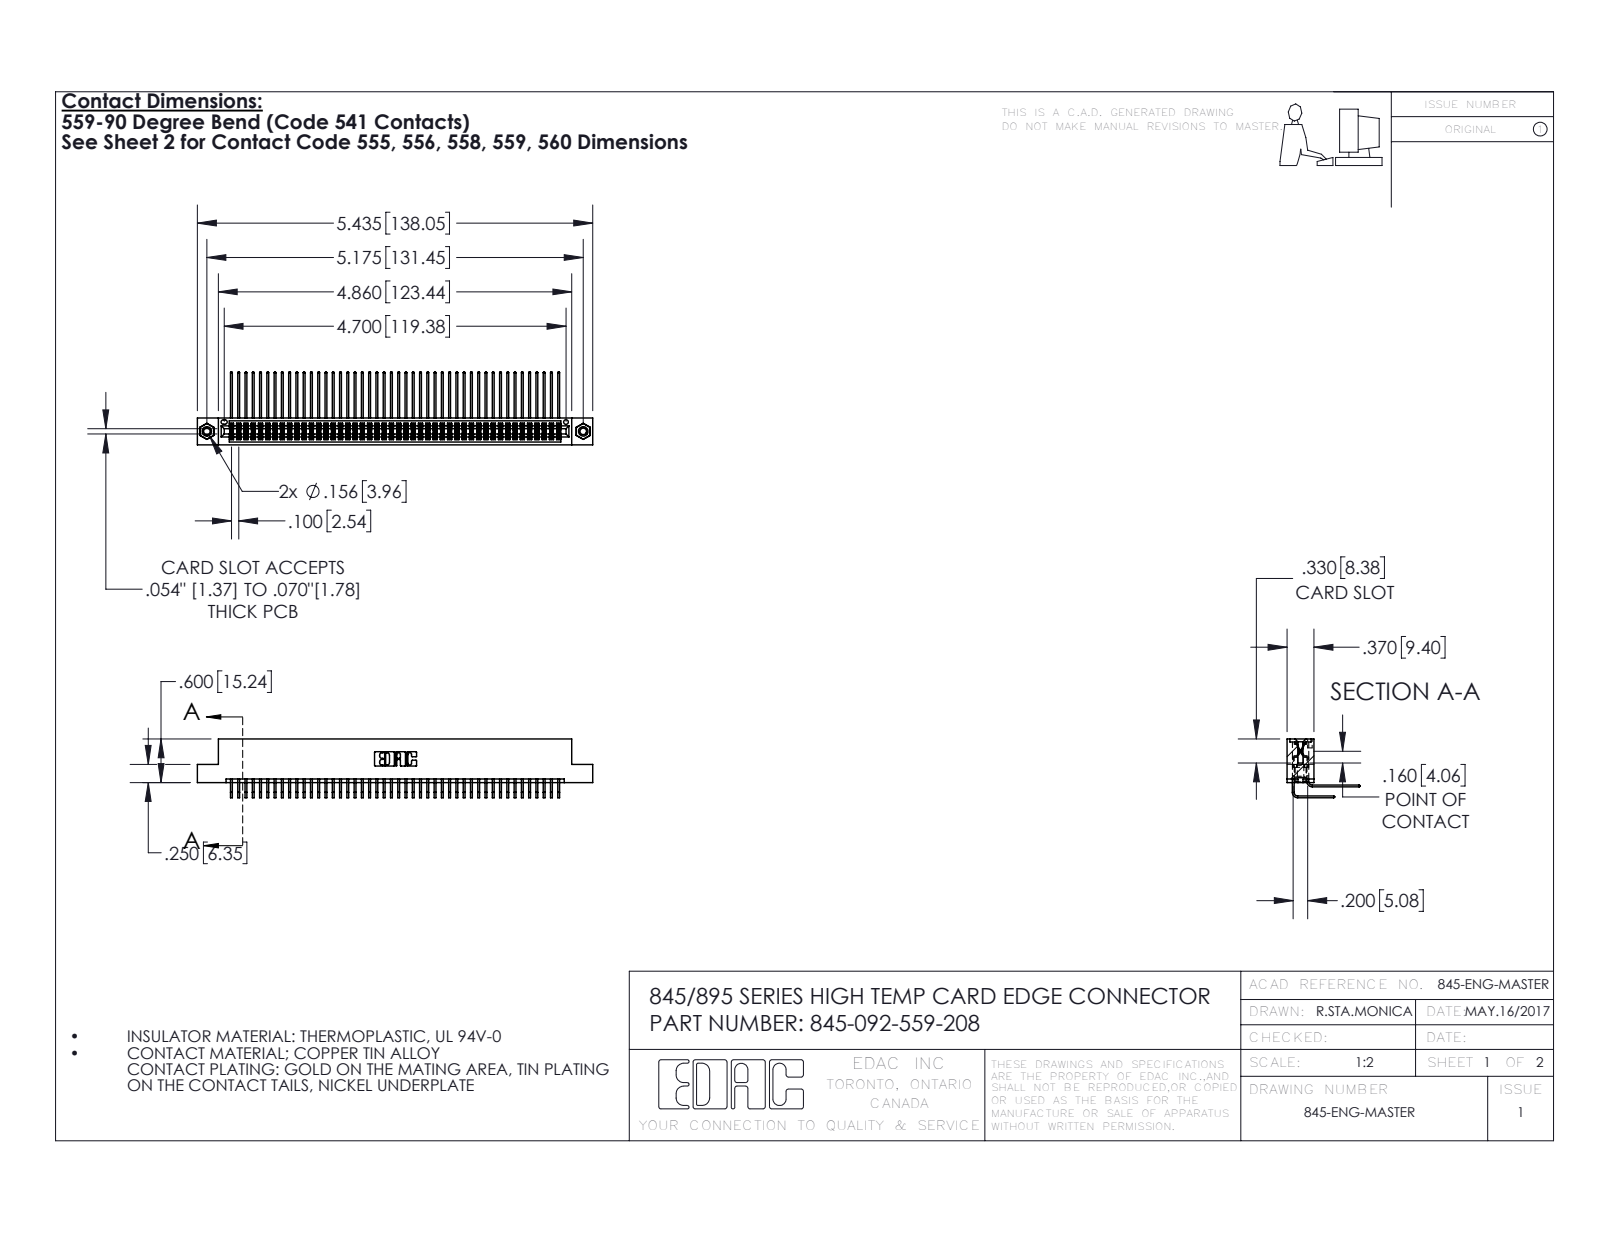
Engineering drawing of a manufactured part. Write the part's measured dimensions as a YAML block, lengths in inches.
part_name: "345-292-001_558 559 Tail - 1; 345 Part_Flush Mounting Lugs - 0.156 Dia-TI; 345-250-001_345-250-003-102; 345-092-559-208 (+1 more)"
step_written_by: "SolidWorks 2016 (CONFIG_CONTROL_DESIGN)"
units: inches
bodies: {solids: 95, faces: 4970, planar: 3332, cylindrical: 1622, other: 16}
overall_size: [5.435, 1.005, 0.809]
volume: 0.853
surface_area: 36.02
round_holes:
  - {diameter: 0.089, count: 2}
  - {diameter: 0.125, count: 2}
  - {diameter: 0.156, count: 2}
  - {diameter: 0.064, count: 1}
round_bosses_or_shafts:
  - {diameter: 0.155, count: 2}
partial_cylinders:
  - {radius: 0.006, count: 139}
  - {radius: 0.01, count: 22}
  - {radius: 0.007, count: 6}
  - {radius: 0.031, count: 6}
  - {radius: 0.026, count: 3}
  - {radius: 0.014, count: 2}
  - {radius: 0.019, count: 2}
  - {radius: 0.022, count: 2}
face_to_face_distances: [0.072, 0.298, 0.2, 0.37, 0.098, 0.272, 0.025, 0.225, 0.175, 0.15]
hole_center_spacings: [0.27, 4.939, 5.175]
